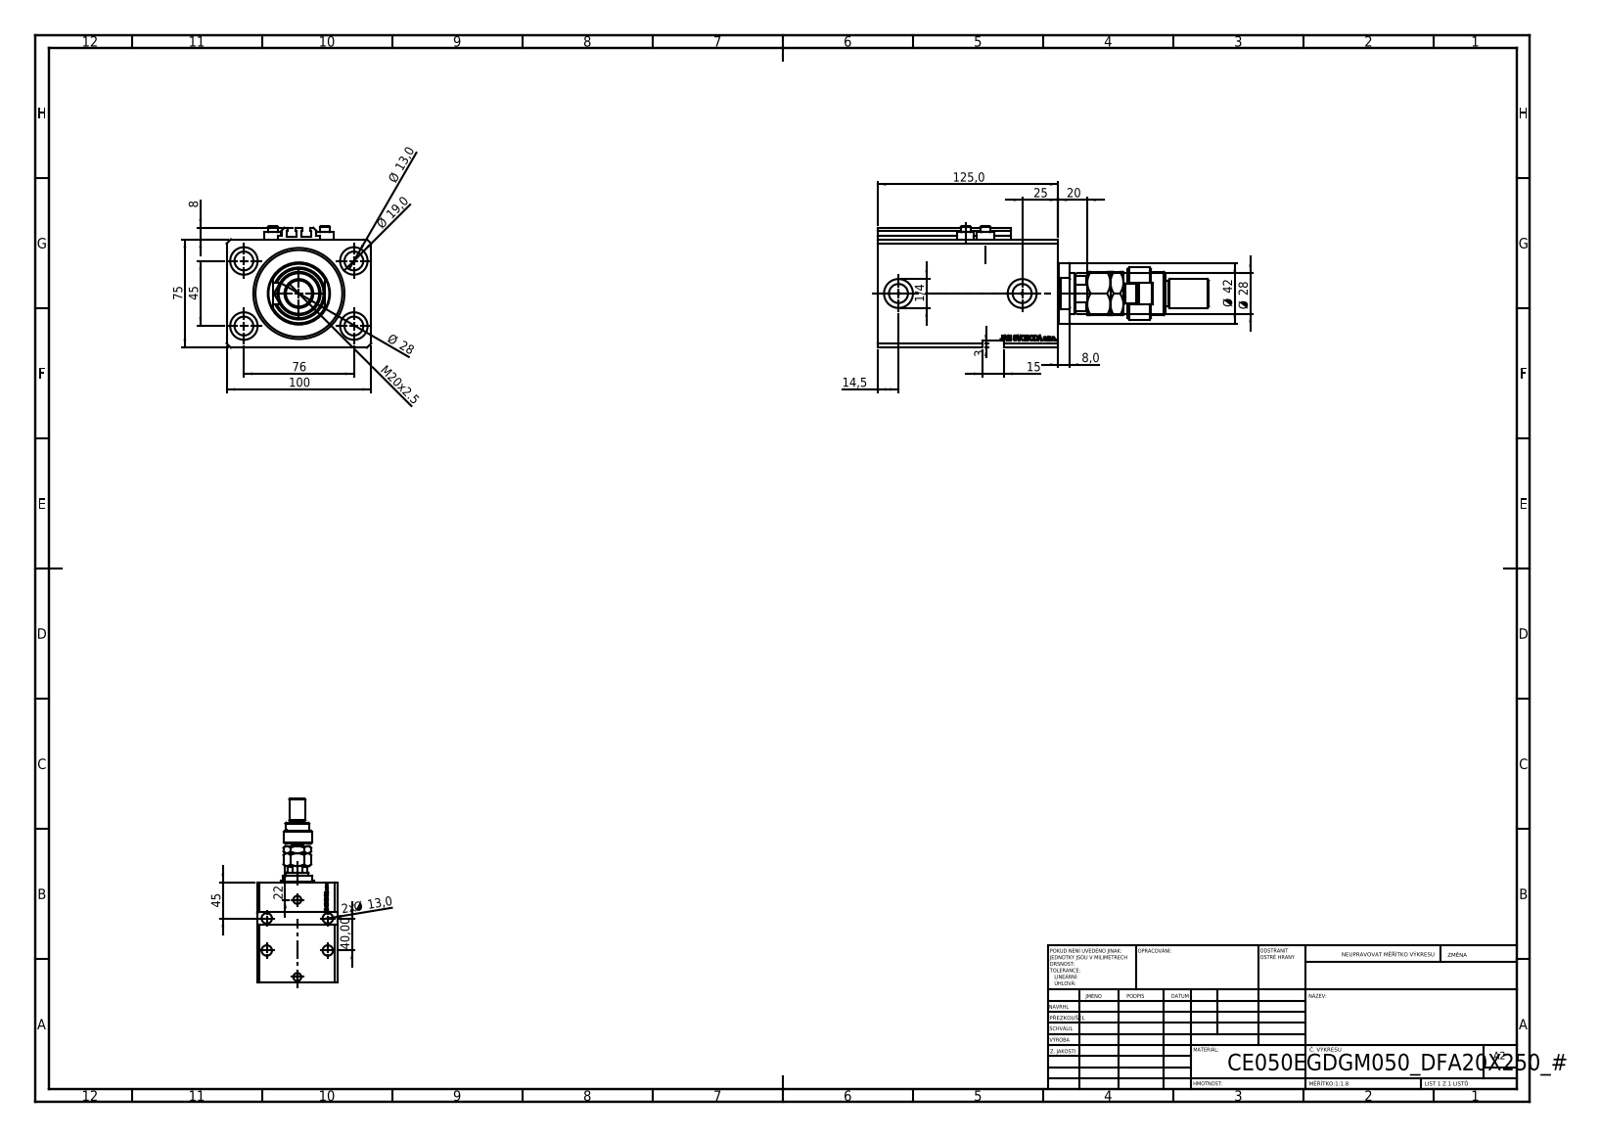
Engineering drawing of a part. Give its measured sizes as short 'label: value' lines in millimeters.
name: V250CE_E_Body; V250CE_VC_E; MFA; ALLEN BOLT V250CE (+2 more)
written by: SolidWorks 2019 (CONFIG_CONTROL_DESIGN)
unit: mm
bodies: 10 solids, 1209 faces (567 planar, 171 cylindrical, 471 other)
size: 229 × 100 × 84
volume: 814 102 mm³; area: 164 768 mm²
holes: 8× ⌀13, 4× ⌀1.25, 4× ⌀4, 4× ⌀19, 2× ⌀10, 2× ⌀13.16, 2× ⌀20, 1× ⌀18.5, 1× ⌀28, 1× ⌀50, 1× ⌀63
bosses: 4× ⌀11.6, 4× ⌀7, 1× ⌀42, 1× ⌀36, 1× ⌀30, 1× ⌀22, 1× ⌀20, 1× ⌀18
rounds: 10× R0.2, 1× R7.5, 1× R12, 1× R13.5
face distances: 75, 100, 20, 125, 11.9, 113.1, 105, 93.1, 70, 55
hole spacings: 44.16, 76, 13.6, 20.72, 27.59, 29, 33.62, 36
